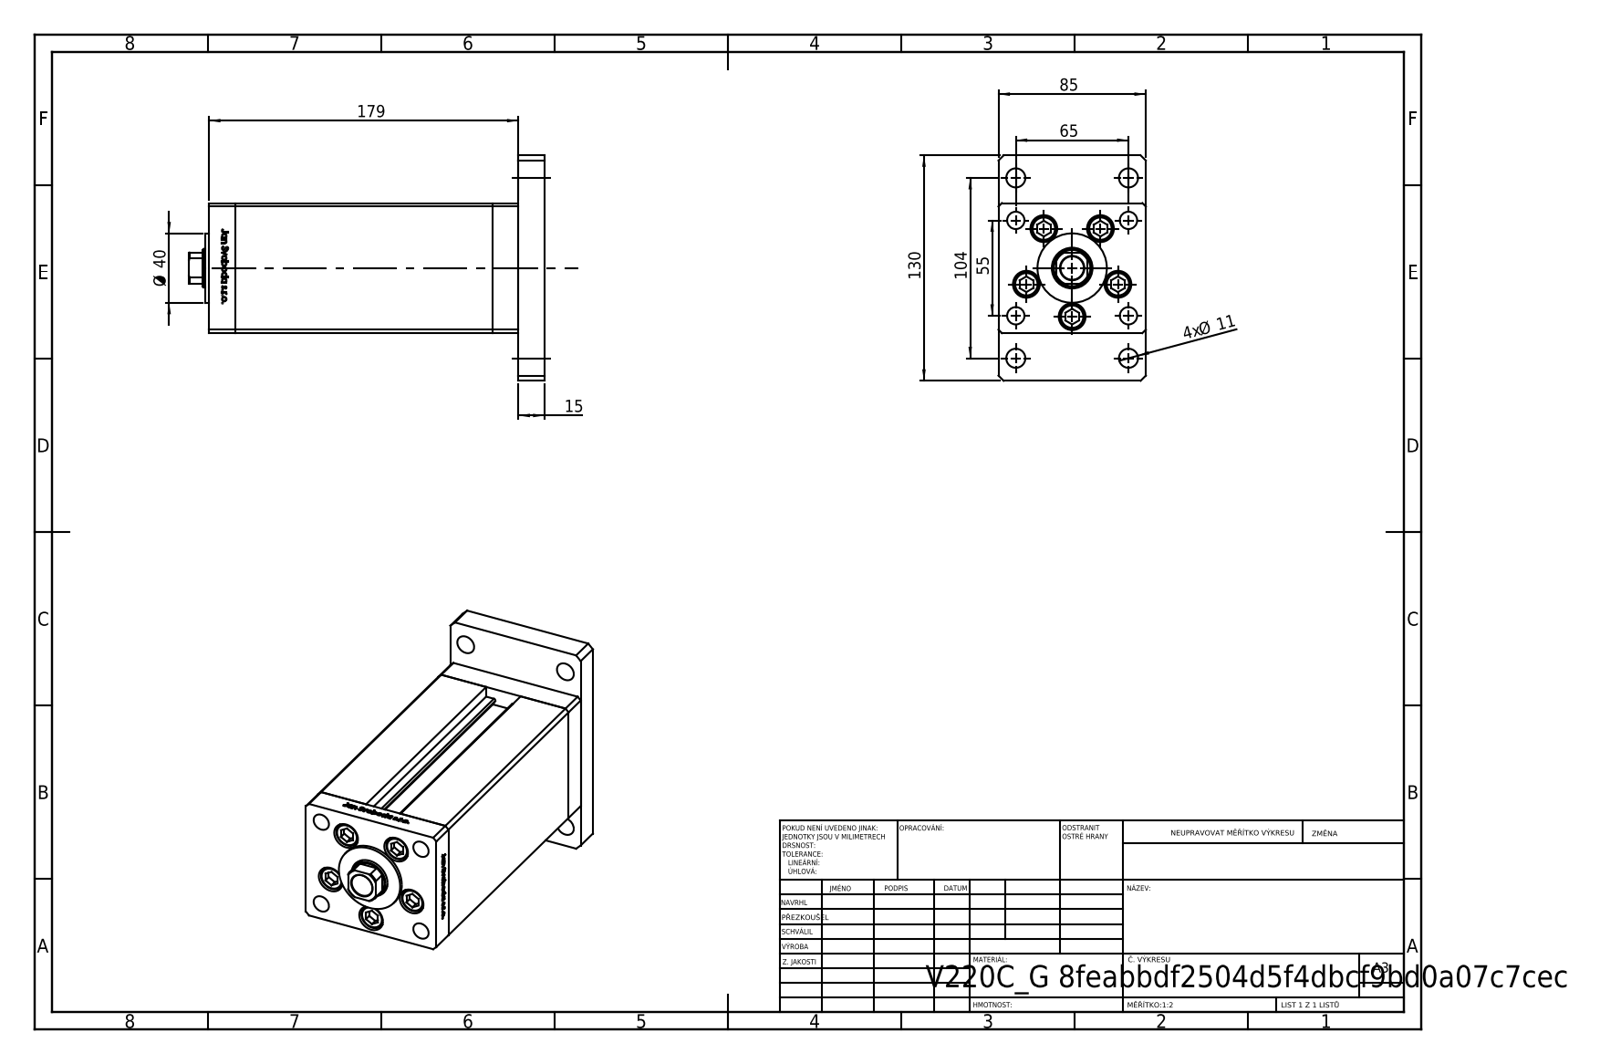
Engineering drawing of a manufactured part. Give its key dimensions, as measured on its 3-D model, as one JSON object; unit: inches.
{"part_name": "V220C_VC_G; V220C BACK_G; ALLEN BOLT; V220C_G_MIDDLE (+2 more)", "step_written_by": "SolidWorks 2019 (CONFIG_CONTROL_DESIGN)", "units": "inches", "bodies": {"solids": 19, "faces": 1301, "planar": 514, "cylindrical": 181, "other": 606}, "overall_size": [8.071, 5.118, 3.346], "volume_in3": 70.91, "surface_area_in2": 304.3, "round_holes": [[0.394, 9], [0.433, 9], [0.61, 5], [0.571, 4], [0.531, 1], [0.866, 1], [0.925, 1], [2.205, 1]], "round_bosses_or_shafts": [[0.315, 9], [0.571, 5], [1.575, 1]], "partial_cylinders_radius": [[0.037, 2], [0.413, 1]], "face_to_face_distances": [0.591, 3.346, 6.437, 7.028, 2.953, 5.846, 1.181, 0.079, 6.949, 7.618], "hole_center_spacings": [1.102, 0.965, 1.676, 2.414, 2.559, 2.735, 3.13, 4.043]}
